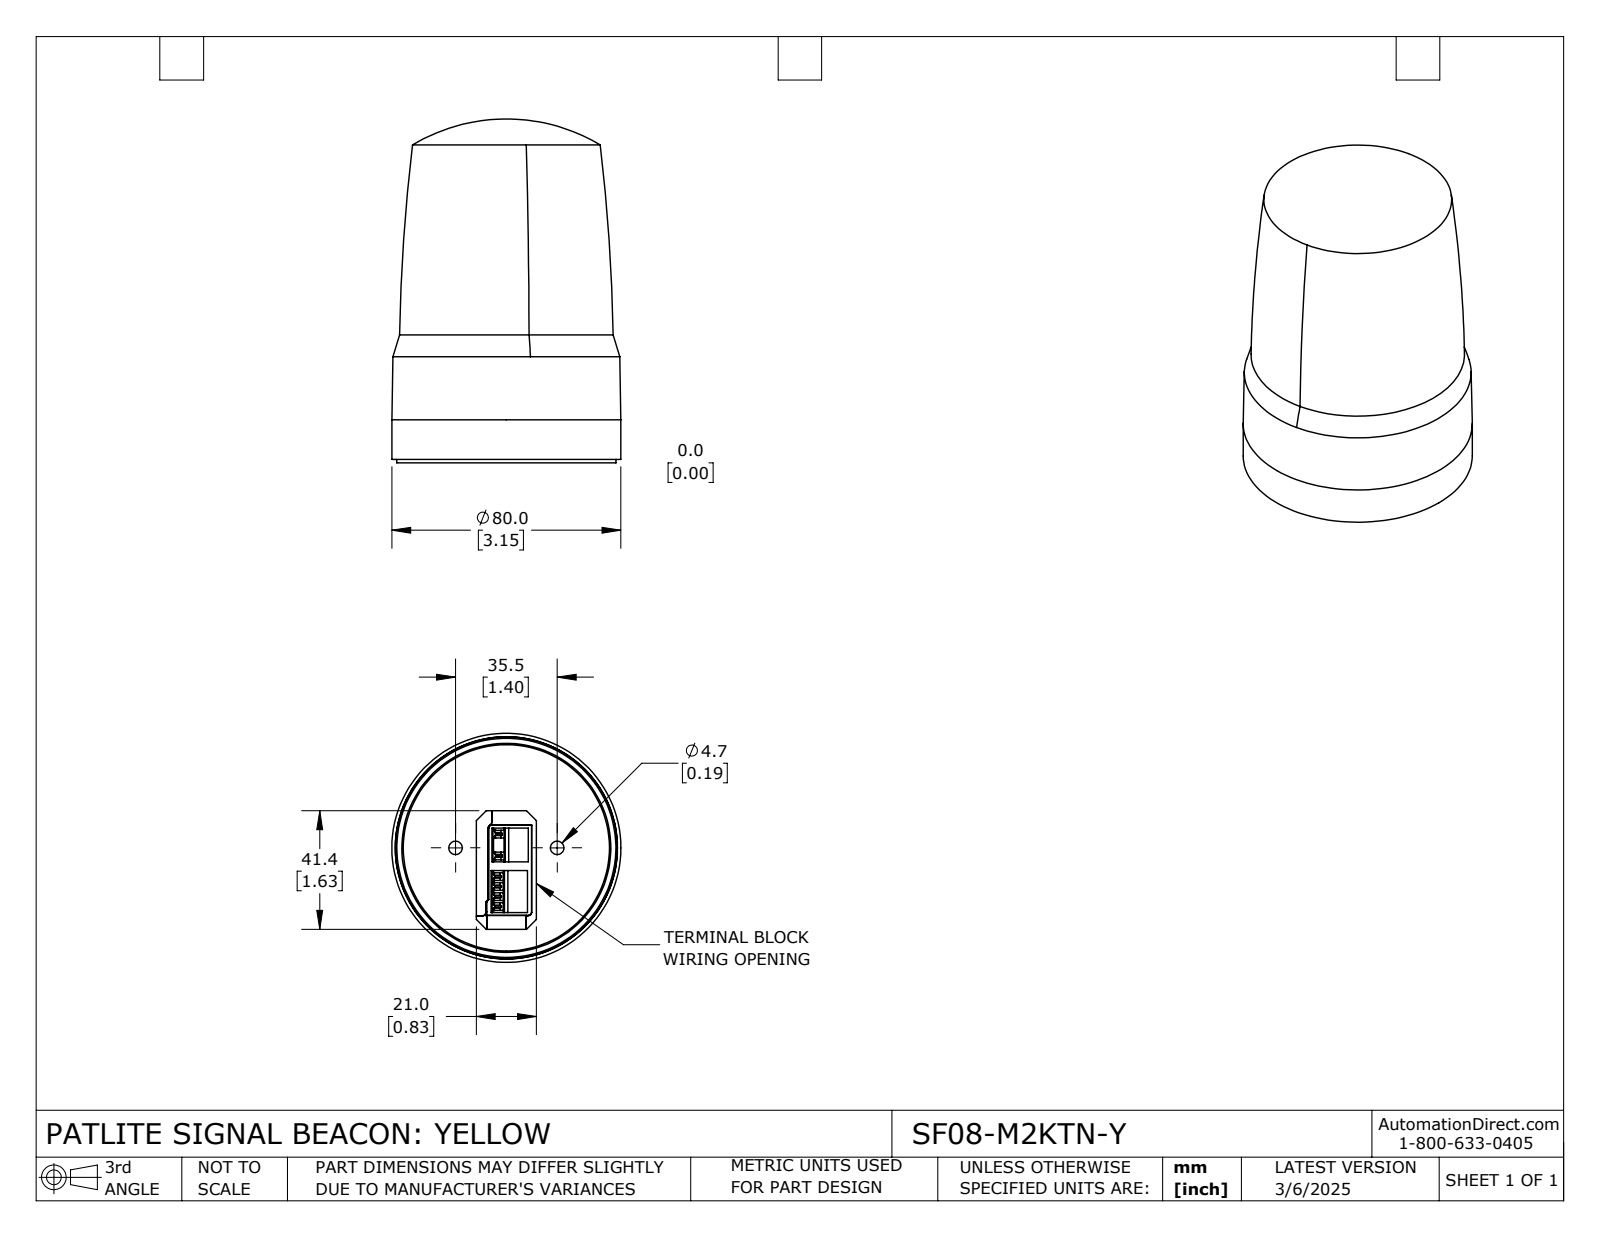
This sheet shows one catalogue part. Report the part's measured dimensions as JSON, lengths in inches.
{"part_name": "SF08-M2KTN-Y", "step_written_by": "SolidWorks 2024 (CONFIG_CONTROL_DESIGN)", "units": "inches", "bodies": {"solids": 2, "faces": 287, "planar": 199, "cylindrical": 23, "other": 65}, "overall_size": [4.724, 3.15, 3.15], "volume_in3": 29.01, "surface_area_in2": 81.21, "round_holes": [[0.185, 2], [0.48, 2], [2.874, 1]], "round_bosses_or_shafts": [[3.15, 1], [3.012, 1], [2.937, 1], [2.835, 1]], "partial_cylinders_radius": [[1.319, 1], [1.362, 1]], "face_to_face_distances": [0.248, 0.185, 0.433, 0.071, 0.504, 0.256, 0.059, 0.374, 0.126, 0.13], "hole_center_spacings": [0.699, 1.398]}
